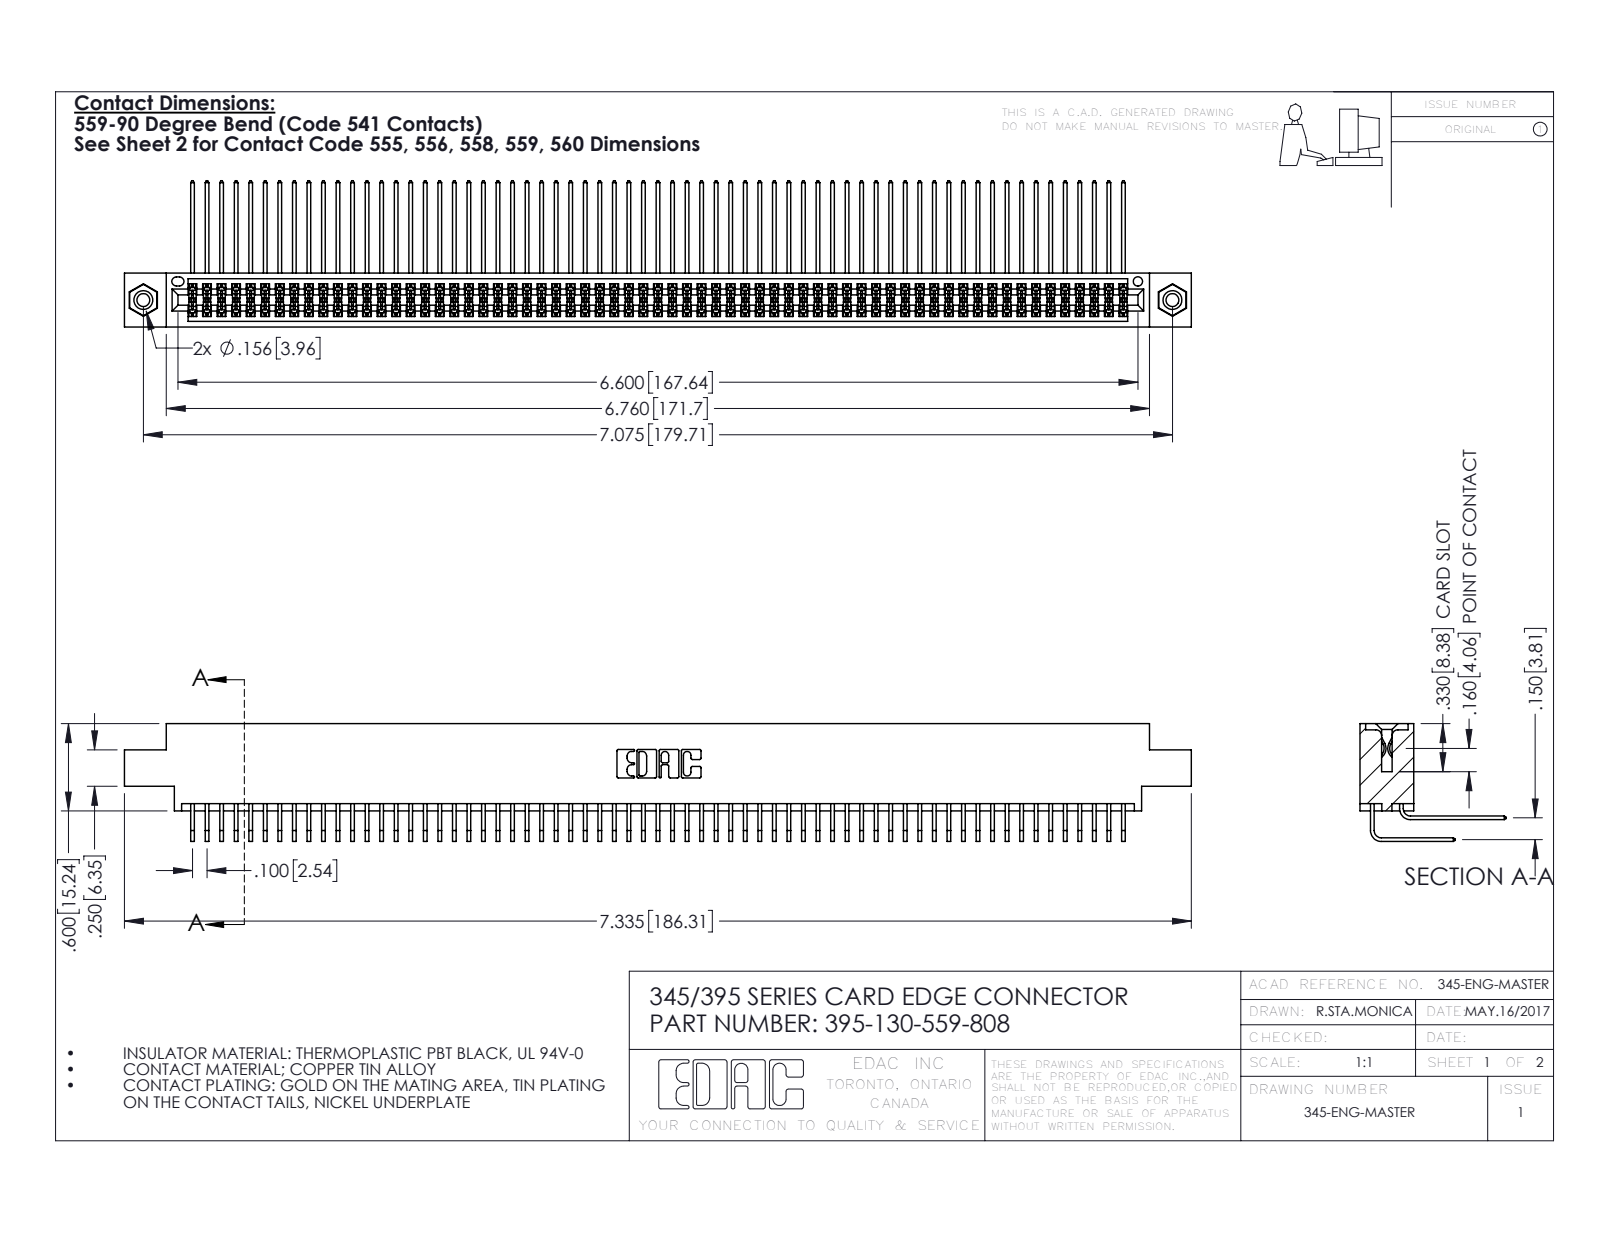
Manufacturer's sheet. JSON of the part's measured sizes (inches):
{"part_name": "345-292-001_559 Tail - 2; 345-292-001_558 559 Tail - 1; 395-130-559-808; 345 Part_0.170 Offset - 0.156 Dia-TI (+1 more)", "step_written_by": "SolidWorks 2016 (CONFIG_CONTROL_DESIGN)", "units": "inches", "bodies": {"solids": 133, "faces": 6950, "planar": 4666, "cylindrical": 2268, "other": 16}, "overall_size": [7.335, 1.005, 0.809], "volume_in3": 1.156, "surface_area_in2": 49.8, "round_holes": [[0.089, 2], [0.125, 2], [0.156, 2], [0.064, 1]], "round_bosses_or_shafts": [[0.155, 2]], "partial_cylinders_radius": [[0.006, 196], [0.01, 22], [0.007, 6], [0.031, 6], [0.026, 3], [0.014, 2], [0.019, 2], [0.022, 2]], "face_to_face_distances": [0.072, 0.298, 0.37, 0.2, 0.098, 0.272, 0.025, 0.225, 0.175, 0.15], "hole_center_spacings": [0.27, 6.839, 7.075]}
